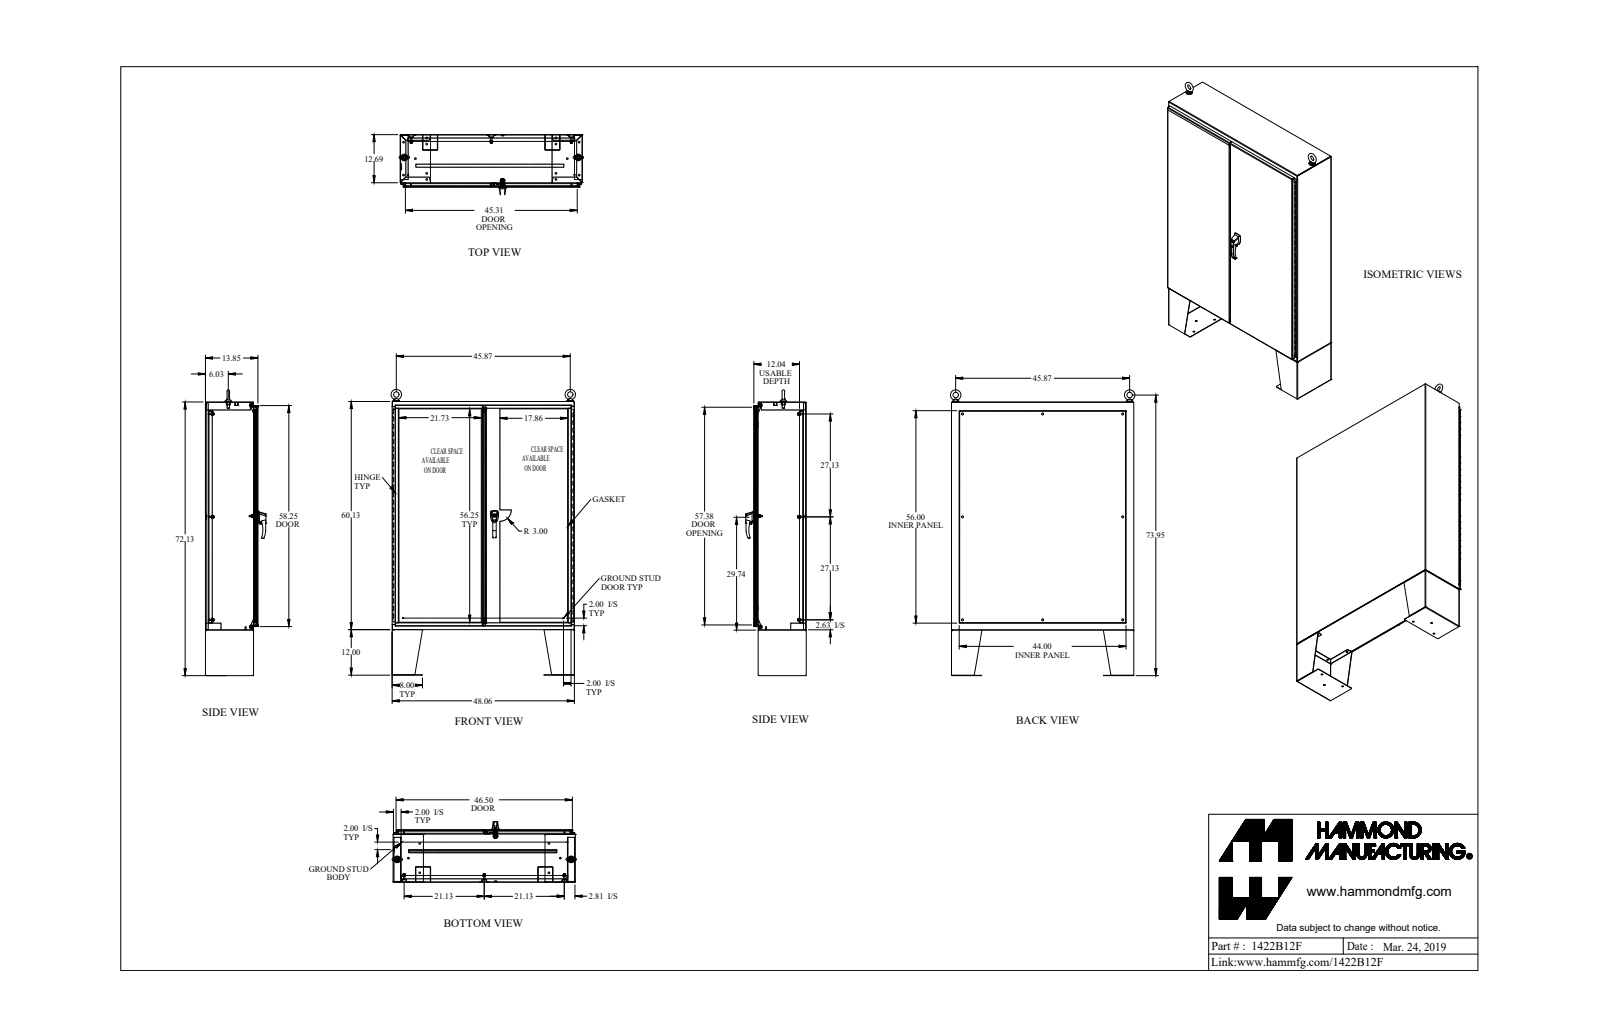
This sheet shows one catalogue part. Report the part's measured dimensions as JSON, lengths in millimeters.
{"part_name": "1422B12F_Default", "step_written_by": "SolidWorks 2019 (CONFIG_CONTROL_DESIGN)", "units": "millimeters", "bodies": {"solids": 90, "faces": 2769, "planar": 1280, "cylindrical": 1242, "other": 247}, "overall_size": [1924.8, 1247.7, 405.5], "volume_mm3": 23380000, "surface_area_mm2": 18320000, "round_holes": [[7.7, 20], [11.1, 14], [7.8, 9], [14.3, 8], [11.3, 6], [2.8, 2], [6.4, 2], [6.5, 2], [7.1, 2], [7.1, 2], [8, 2], [9.9, 2]], "round_bosses_or_shafts": [[25.4, 10], [16.5, 8], [9.5, 8], [8.4, 8], [7.1, 6], [6.4, 4], [44.5, 2], [38.1, 2]], "partial_cylinders_radius": [[1.2, 32], [3.6, 32], [3.2, 22], [0.5, 16], [1.5, 14], [2.9, 12], [1.3, 8], [4.7, 8]], "face_to_face_distances": [2.4, 2.4, 346.9, 349.3, 349.3, 351.7, 3.2, 306.5, 304.1, 42.8], "hole_center_spacings": [152.4, 1188.2, 304.8, 1217.1, 457.2, 1264, 609.6, 1326.7]}
